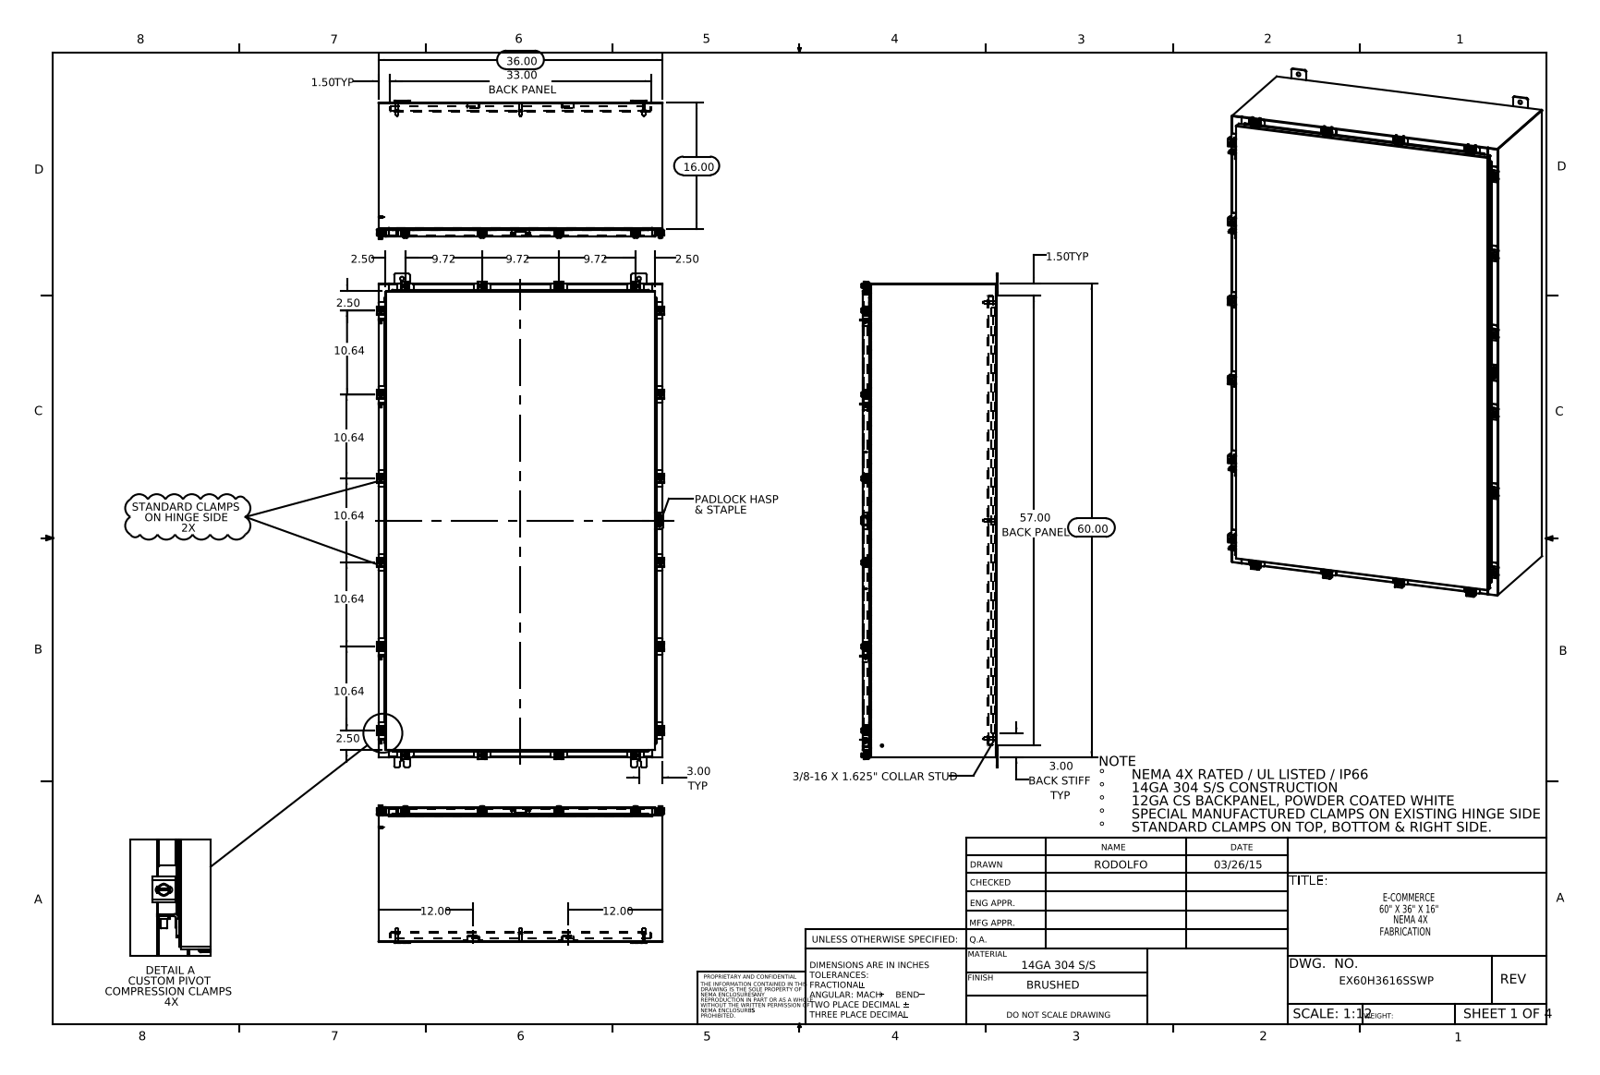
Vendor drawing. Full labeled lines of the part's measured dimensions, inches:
Part name (STEP PRODUCT): EX60H3616SSWP; N-WMT04X30402202210-00 22104005_DEFAULT; EX60H3616SSWP Clamp Bracket; N-WMT04X30402202210-00 22101002 (+8 more)
STEP written by: SolidWorks 2014 (CONFIG_CONTROL_DESIGN)
Units: inches
Bodies: 140 solids, 3424 faces (1773 planar, 1319 cylindrical, 332 other)
Overall size (bounding box): 62.5 × 36.421 × 17.453
Volume: 850 in³ · Surface area: 21 217 in²
Round holes (diameter × count): ⌀0.213 ×20, ⌀0.26 ×20, ⌀0.5 ×12, ⌀0.25 ×9, ⌀0.125 ×1
Round bosses / shafts (diameter × count): ⌀0.5 ×20, ⌀0.25 ×20, ⌀0.399 ×16, ⌀0.625 ×8, ⌀0.375 ×8, ⌀0.33 ×8, ⌀0.157 ×8, ⌀0.14 ×8
Partial cylindrical surfaces — rounded edges, fillets, slot ends (radius × count): R0.06 ×84, R0.141 ×40, R0.013 ×38, R0.12 ×36, R0.088 ×34, R0.09 ×32, R0.05 ×29, R0.145 ×28
Main face-to-face distances: 0.075, 16.9, 16.826, 0.104, 16.975, 35.925, 1, 1.075, 15.826, 15.9
Hole centre spacings: 1.969, 2.224, 2.347, 13.972, 14.729, 16.126, 27.625, 29.744
